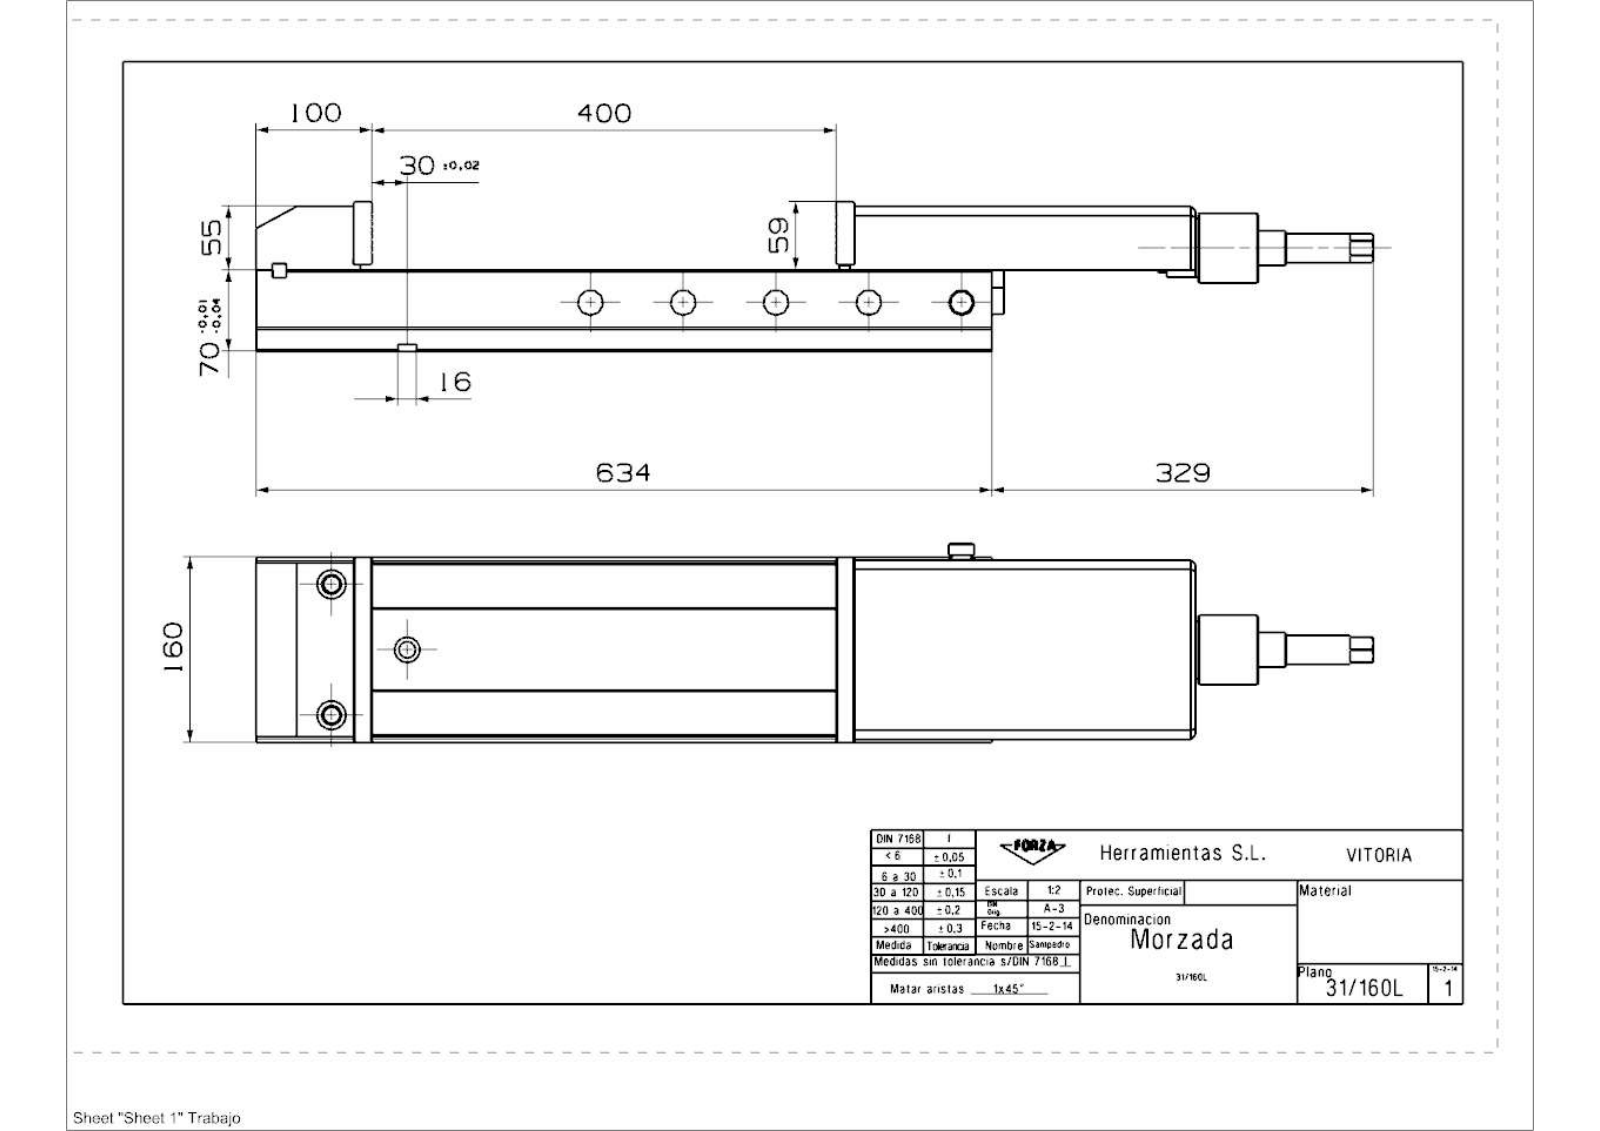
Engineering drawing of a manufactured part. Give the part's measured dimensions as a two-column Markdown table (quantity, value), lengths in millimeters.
| quantity | value |
| --- | --- |
| part name | 31_160L_Mordaza |
| STEP written by | SIEMENS PLM Software NX 9.0 (CONFIG_CONTROL_DESIGN) |
| units | millimeters |
| bodies | 18 solids, 529 faces (332 planar, 112 cylindrical, 85 other) |
| overall size | 963.18 × 171.8 × 129 |
| volume | 7 727 000 mm³ |
| surface area | 891 463 mm² |
| round holes (diameter × count) | 22 × 9, 5.19 × 4, 9 × 4, 14 × 4, 14.38 × 4, 17 × 4, 3.43 × 2, 4 × 2, 4.5 × 2, 6.99 × 2, 8.78 × 2, 11 × 2 |
| round bosses / shafts (diameter × count) | 60 × 1, 52 × 1, 50 × 1, 30 × 1, 28.6 × 1, 26 × 1, 25 × 1, 24 × 1 |
| partial cylindrical surfaces (radius × count) | 10 × 4, 2 × 2, 6.5 × 2, 8 × 2, 25 × 1, 32 × 1 |
| main face-to-face distances | 70, 125, 41, 55, 29, 2.5, 96, 5, 155, 150 |
| hole center spacings | 25, 113, 80, 20, 115.73, 160, 4, 7 |
